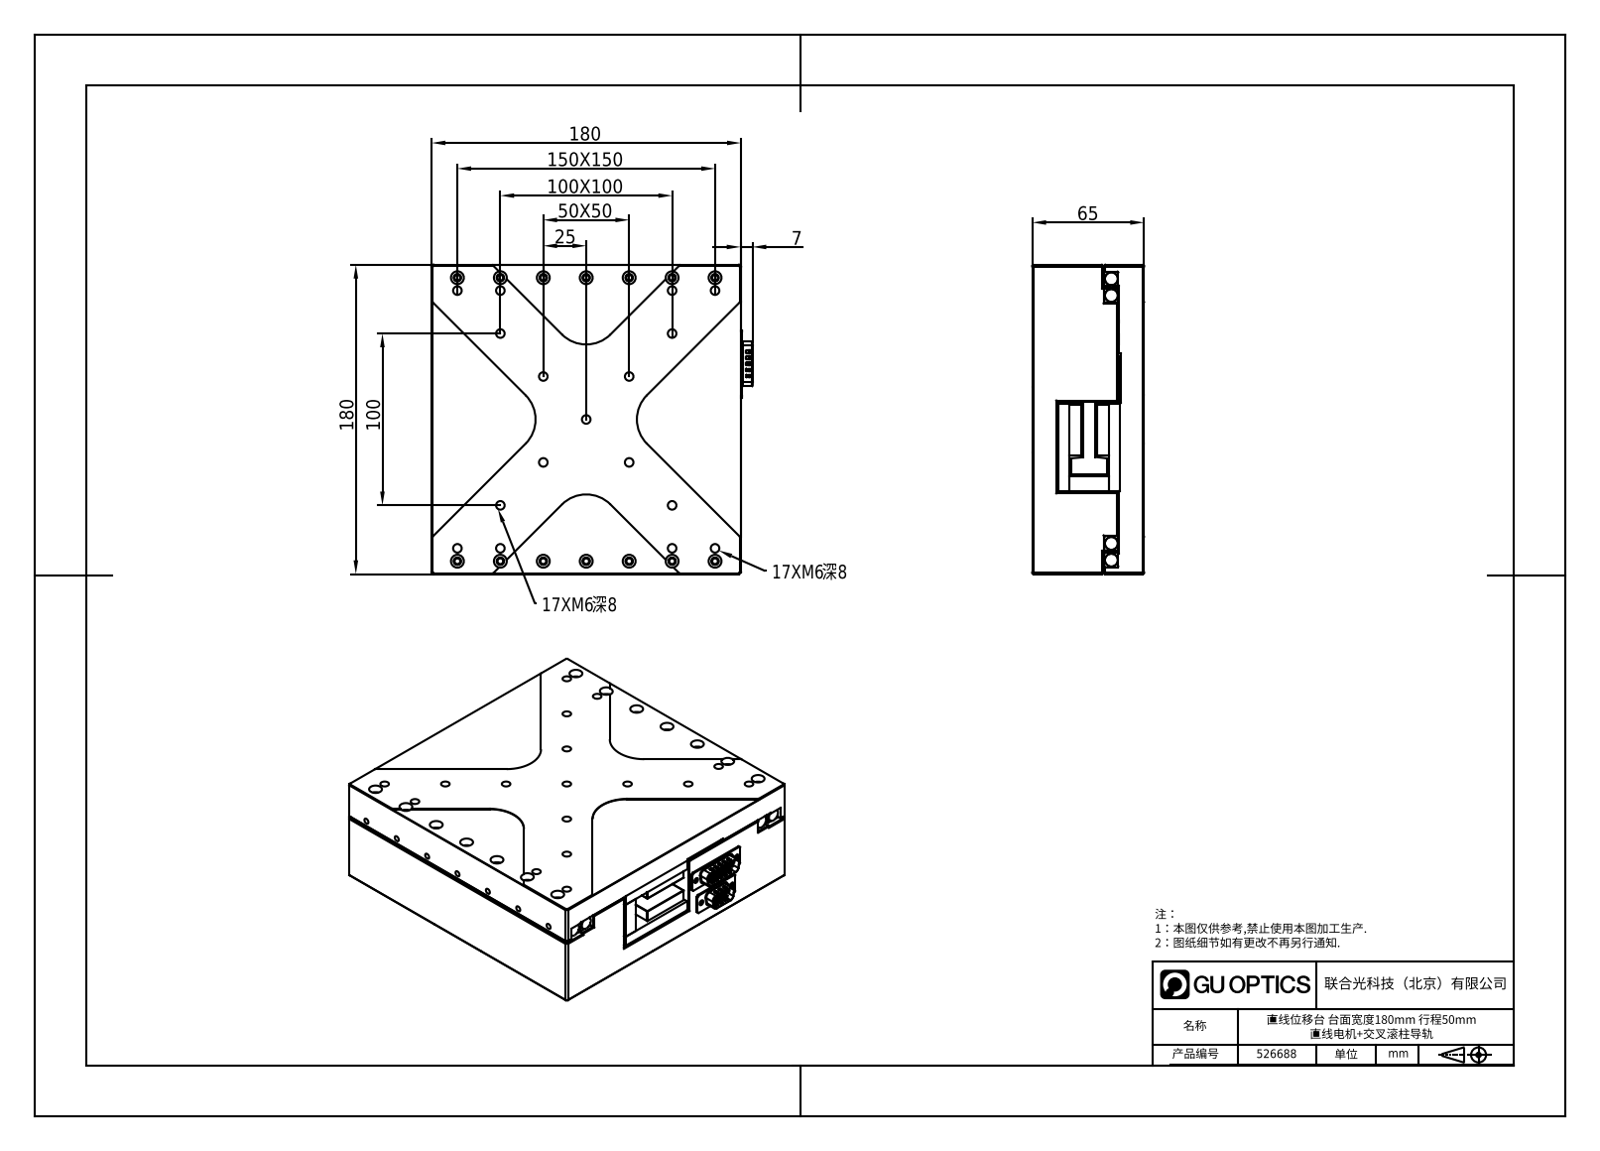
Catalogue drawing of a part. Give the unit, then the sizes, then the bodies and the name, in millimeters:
Units: millimetres
Overall size (bounding box): 186.8 × 180 × 65
Round holes (diameter × count): ⌀3.3 ×50, ⌀6 ×28, ⌀7.5 ×24, ⌀2.5 ×18, ⌀5 ×17, ⌀4.3 ×14, ⌀4.5 ×13, ⌀8 ×13, ⌀1.1 ×9, ⌀1.5 ×8, ⌀2 ×8, ⌀4.2 ×6
Round bosses / shafts (diameter × count): ⌀3 ×48, ⌀1 ×35, ⌀0.6 ×26, ⌀1.5 ×9, ⌀7 ×6, ⌀3.5 ×2, ⌀8.95 ×1, ⌀5.6 ×1
Partial cylindrical surfaces — rounded edges, fillets, slot ends (radius × count): R0.2 ×66, R1 ×38, R2 ×29, R0.4 ×16, R0.45 ×10, R0.3 ×8, R0.8 ×8, R1.3 ×8
Main face-to-face distances: 64.7, 50.5, 0.75, 14.5, 50.2, 14.2, 15, 0.5, 14.25, 180
Hole centre spacings: 25, 30, 60, 75, 50, 3.16, 2.77, 15
Volume: 1 873 000 mm³ · Surface area: 365 728 mm²
Bodies: 22 solids, 3075 faces (1374 planar, 1023 cylindrical, 678 other)
Part name (STEP PRODUCT): 526688
STEP written by: SolidWorks 2020 (CONFIG_CONTROL_DESIGN)
